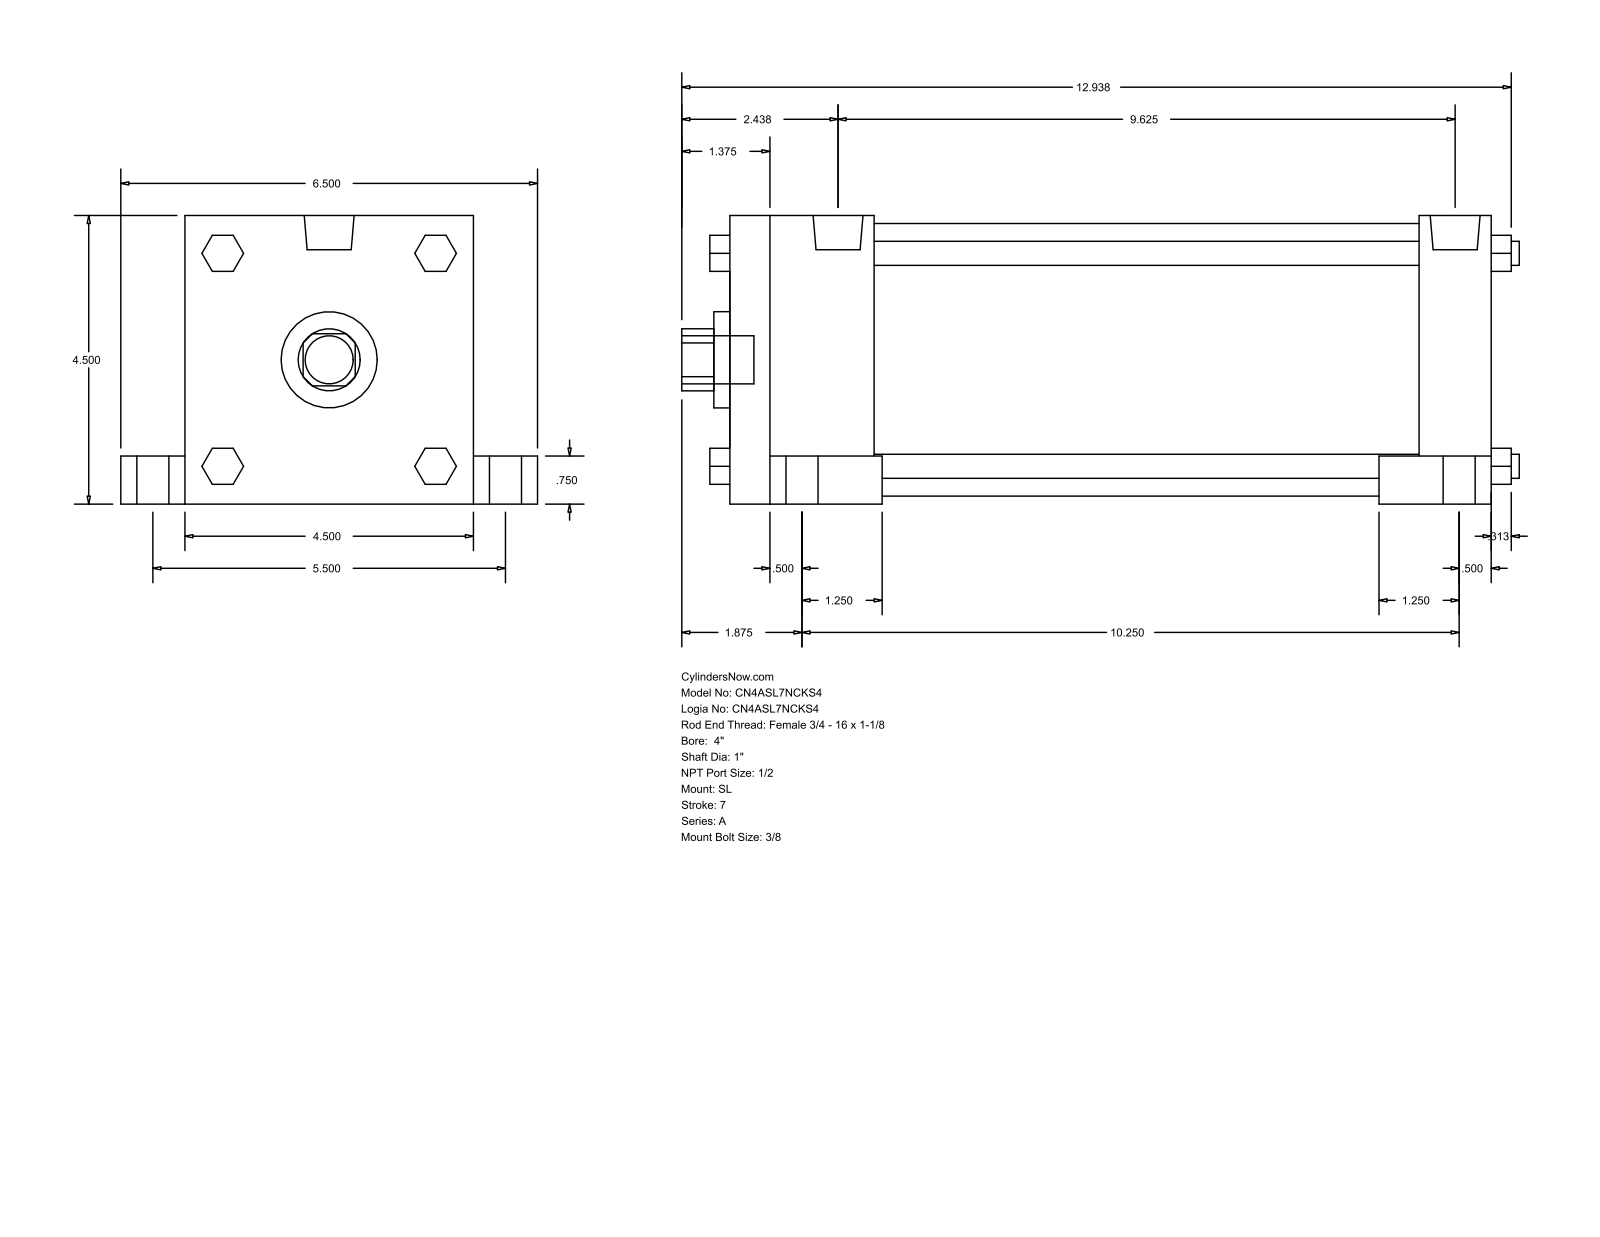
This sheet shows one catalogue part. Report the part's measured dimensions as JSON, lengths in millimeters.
{"part_name": "A_SL__0400_1", "step_written_by": "GSSL Pune (CONFIG_CONTROL_DESIGN)", "units": "millimeters", "bodies": {"solids": 0, "faces": 150, "planar": 114, "cylindrical": 36, "other": 0}, "overall_size": [331.79, 165.1, 114.3], "round_holes": [[25.4, 1], [38.1, 1], [107.95, 1]], "round_bosses_or_shafts": [[19.05, 5], [12.7, 4], [9.53, 4], [8.73, 4], [19.77, 2]], "partial_cylinders_radius": [[12.29, 1]], "face_to_face_distances": [114.3, 301.63, 57.15, 244.48, 273.05, 215.9, 28.58, 19.05, 25.4, 139.7]}
